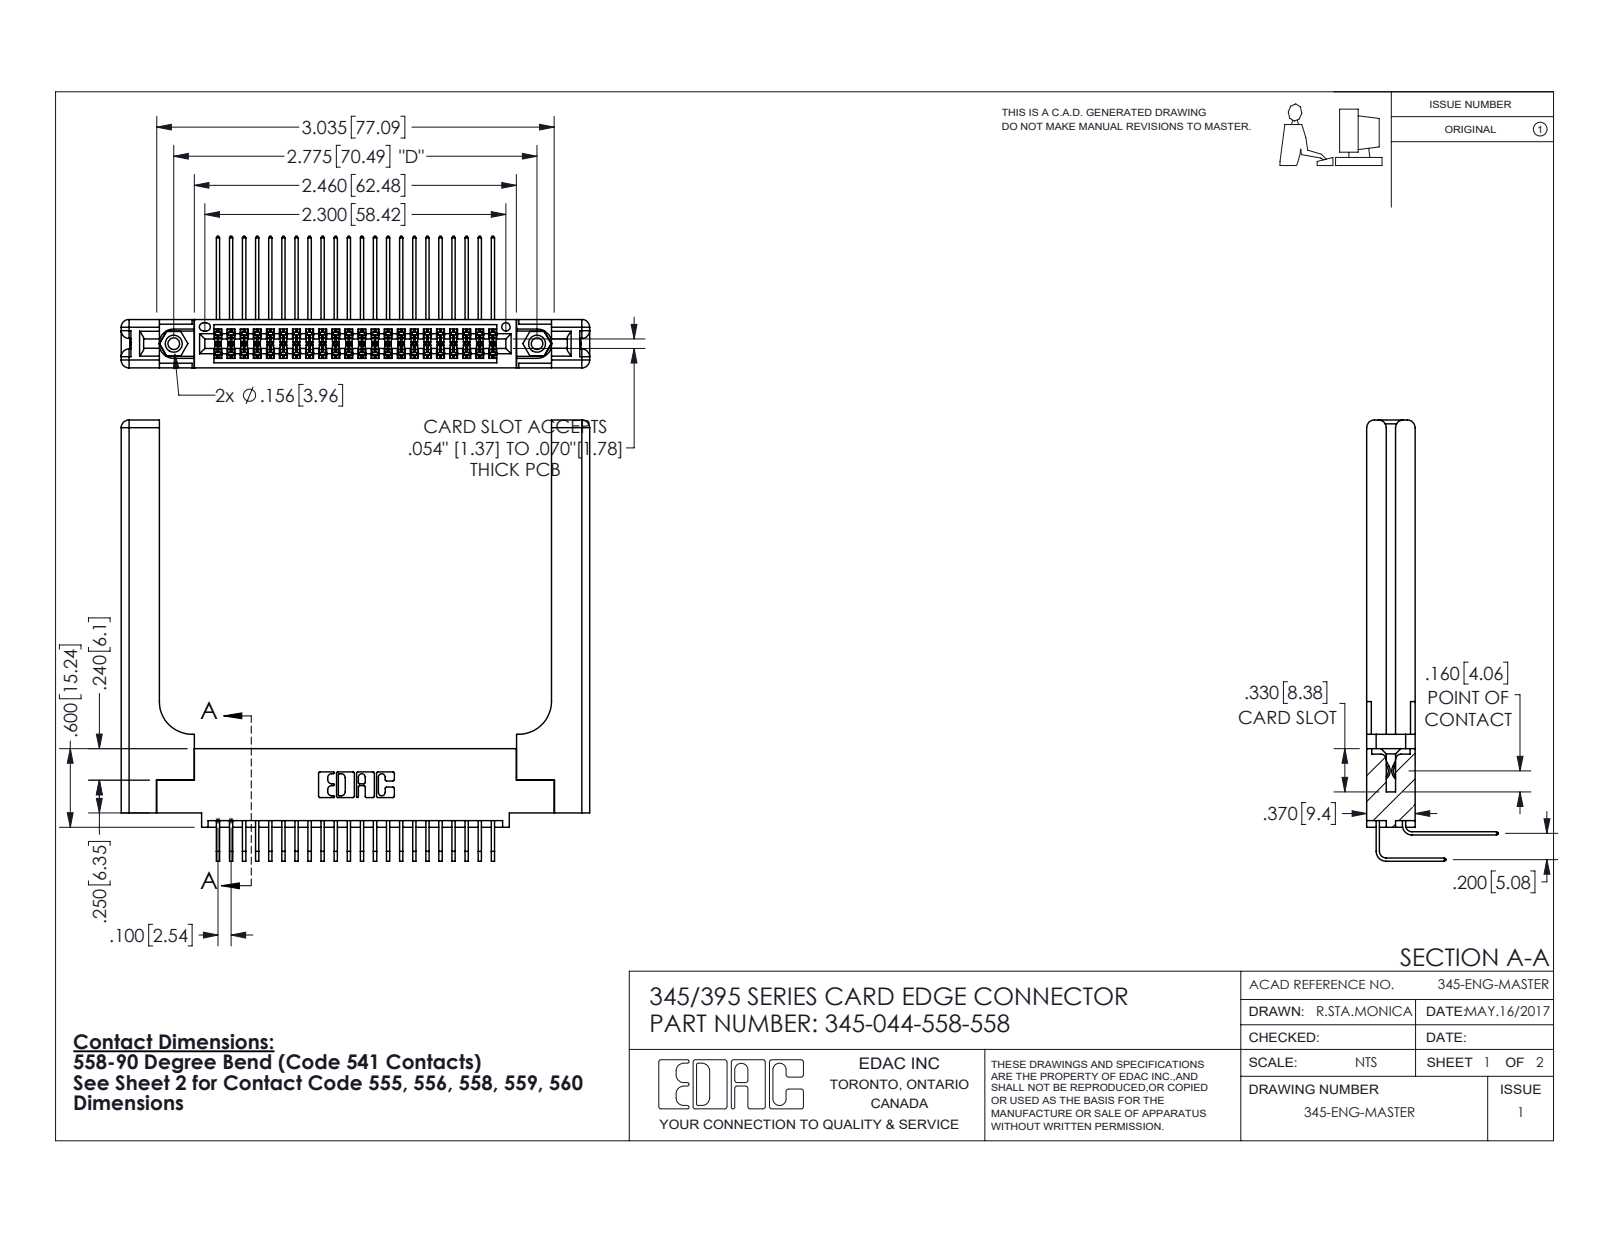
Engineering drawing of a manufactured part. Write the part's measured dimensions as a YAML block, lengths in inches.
part_name: "345-250-001_345-250-001-102; 345-292-001_558 559 Tail - 1; 345-292-001_558 Tail - 2; 345-220-058_345-220-058 (+2 more)"
step_written_by: "SolidWorks 2016 (CONFIG_CONTROL_DESIGN)"
units: inches
bodies: {solids: 49, faces: 2674, planar: 1772, cylindrical: 842, other: 60}
overall_size: [3.579, 3.369, 1.005]
volume: 1.056
surface_area: 29.46
round_holes:
  - {diameter: 0.089, count: 2}
  - {diameter: 0.125, count: 2}
  - {diameter: 0.156, count: 2}
  - {diameter: 0.064, count: 1}
round_bosses_or_shafts:
  - {diameter: 0.155, count: 2}
partial_cylinders:
  - {radius: 0.006, count: 88}
  - {radius: 0.01, count: 22}
  - {radius: 0.06, count: 16}
  - {radius: 0.007, count: 6}
  - {radius: 0.031, count: 6}
  - {radius: 0.026, count: 3}
  - {radius: 0.014, count: 2}
  - {radius: 0.019, count: 2}
face_to_face_distances: [0.37, 0.072, 0.298, 0.2, 0.15, 0.148, 0.077, 0.098, 0.272, 0.025]
hole_center_spacings: [0.27, 2.541, 2.775]
